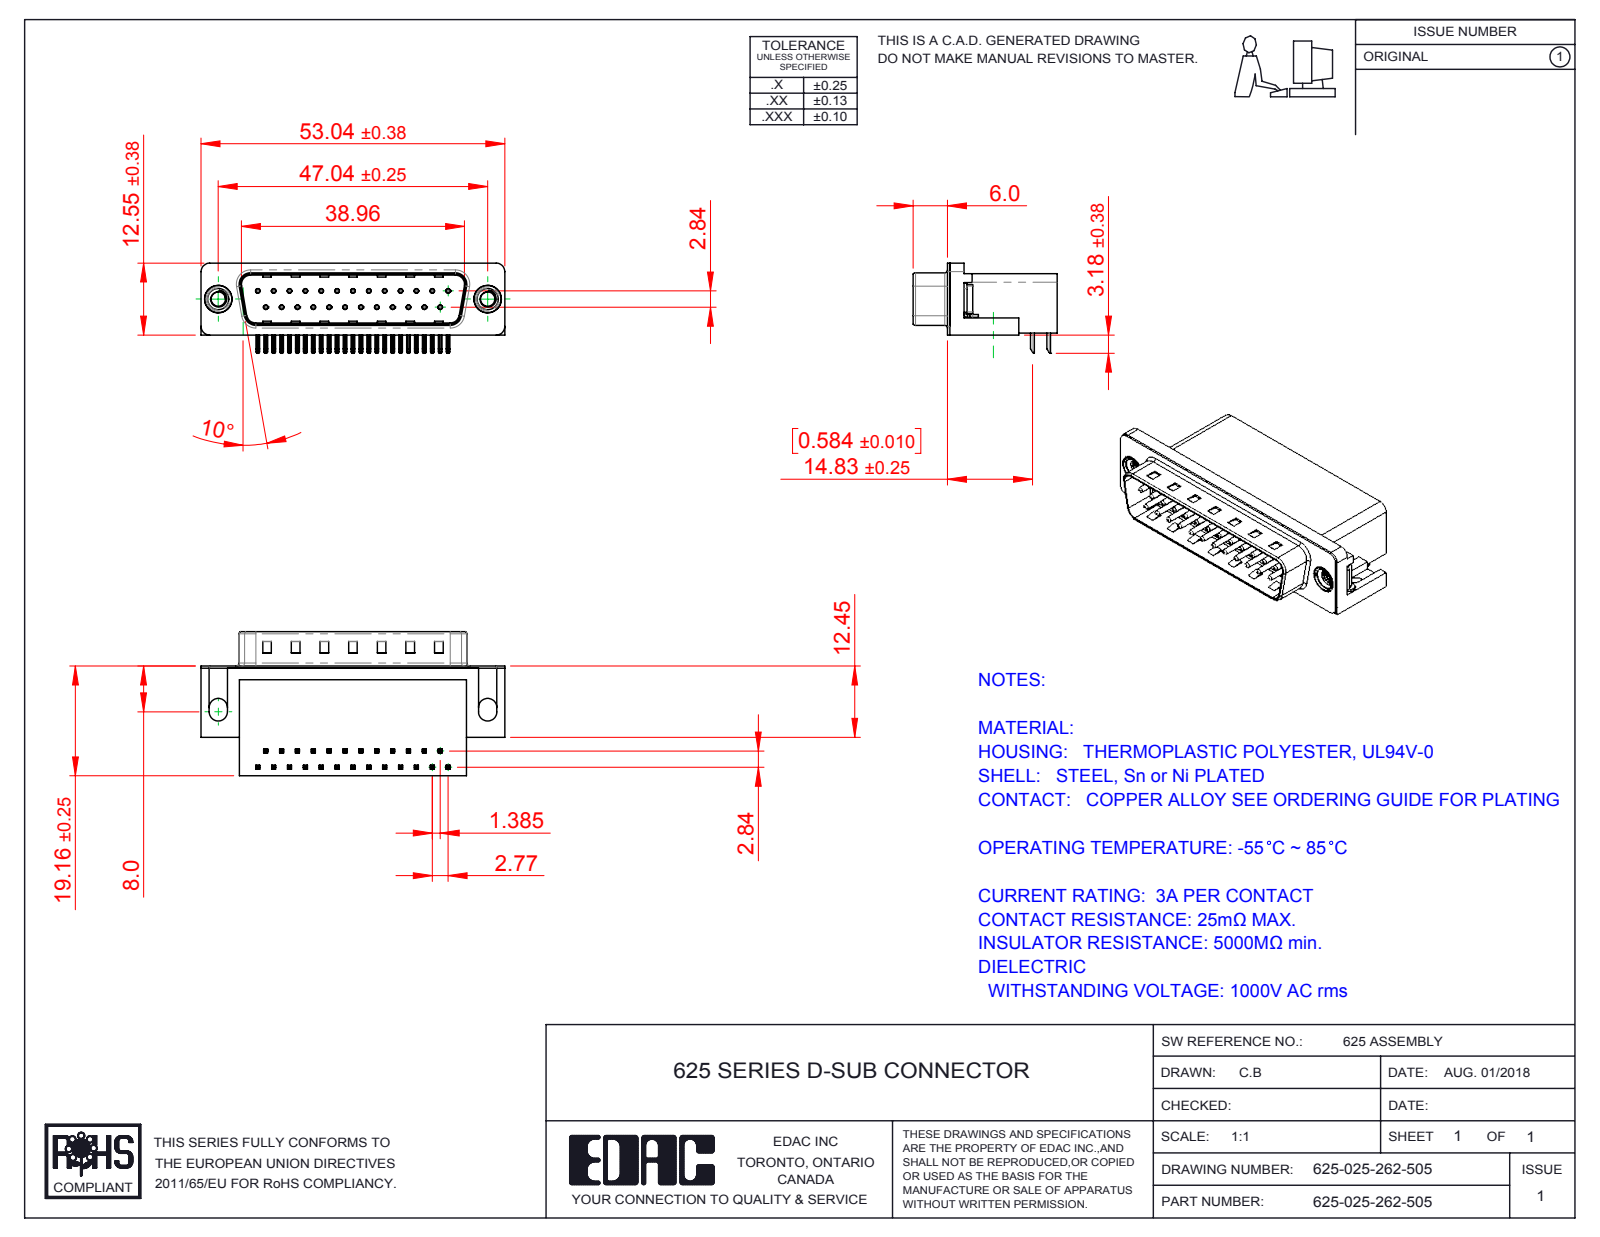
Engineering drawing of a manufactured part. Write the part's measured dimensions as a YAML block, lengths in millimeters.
part_name: "625 M3 Threaded Rivet; 625 Non Board Mount; 625 Contact Bottom; 625 Shell_25 Socket (+3 more)"
step_written_by: "SolidWorks 2016 (CONFIG_CONTROL_DESIGN)"
units: millimeters
bodies: {solids: 31, faces: 2263, planar: 1407, cylindrical: 661, other: 195}
overall_size: [53.04, 25.16, 15.73]
volume: 9131
surface_area: 8731
round_holes:
  - {diameter: 0.35, count: 25}
  - {diameter: 0.8, count: 25}
  - {diameter: 2.5, count: 2}
  - {diameter: 4, count: 2}
  - {diameter: 4.8, count: 2}
  - {diameter: 5, count: 2}
round_bosses_or_shafts:
  - {diameter: 0.75, count: 25}
  - {diameter: 4.9, count: 2}
  - {diameter: 4.75, count: 2}
  - {diameter: 3.9, count: 2}
partial_cylinders:
  - {radius: 0.25, count: 108}
  - {radius: 0.12, count: 50}
  - {radius: 1, count: 16}
  - {radius: 0.5, count: 9}
  - {radius: 1.6, count: 8}
  - {radius: 1.5, count: 7}
  - {radius: 0.9, count: 4}
  - {radius: 2, count: 4}
face_to_face_distances: [0.4, 10.35, 18.76, 2.1, 8.76, 10.46, 10.86, 1.7, 19.16, 10.11]
hole_center_spacings: [3.16, 2.77, 11.08, 5.54, 8.31, 5.03, 13.85, 7.48]
